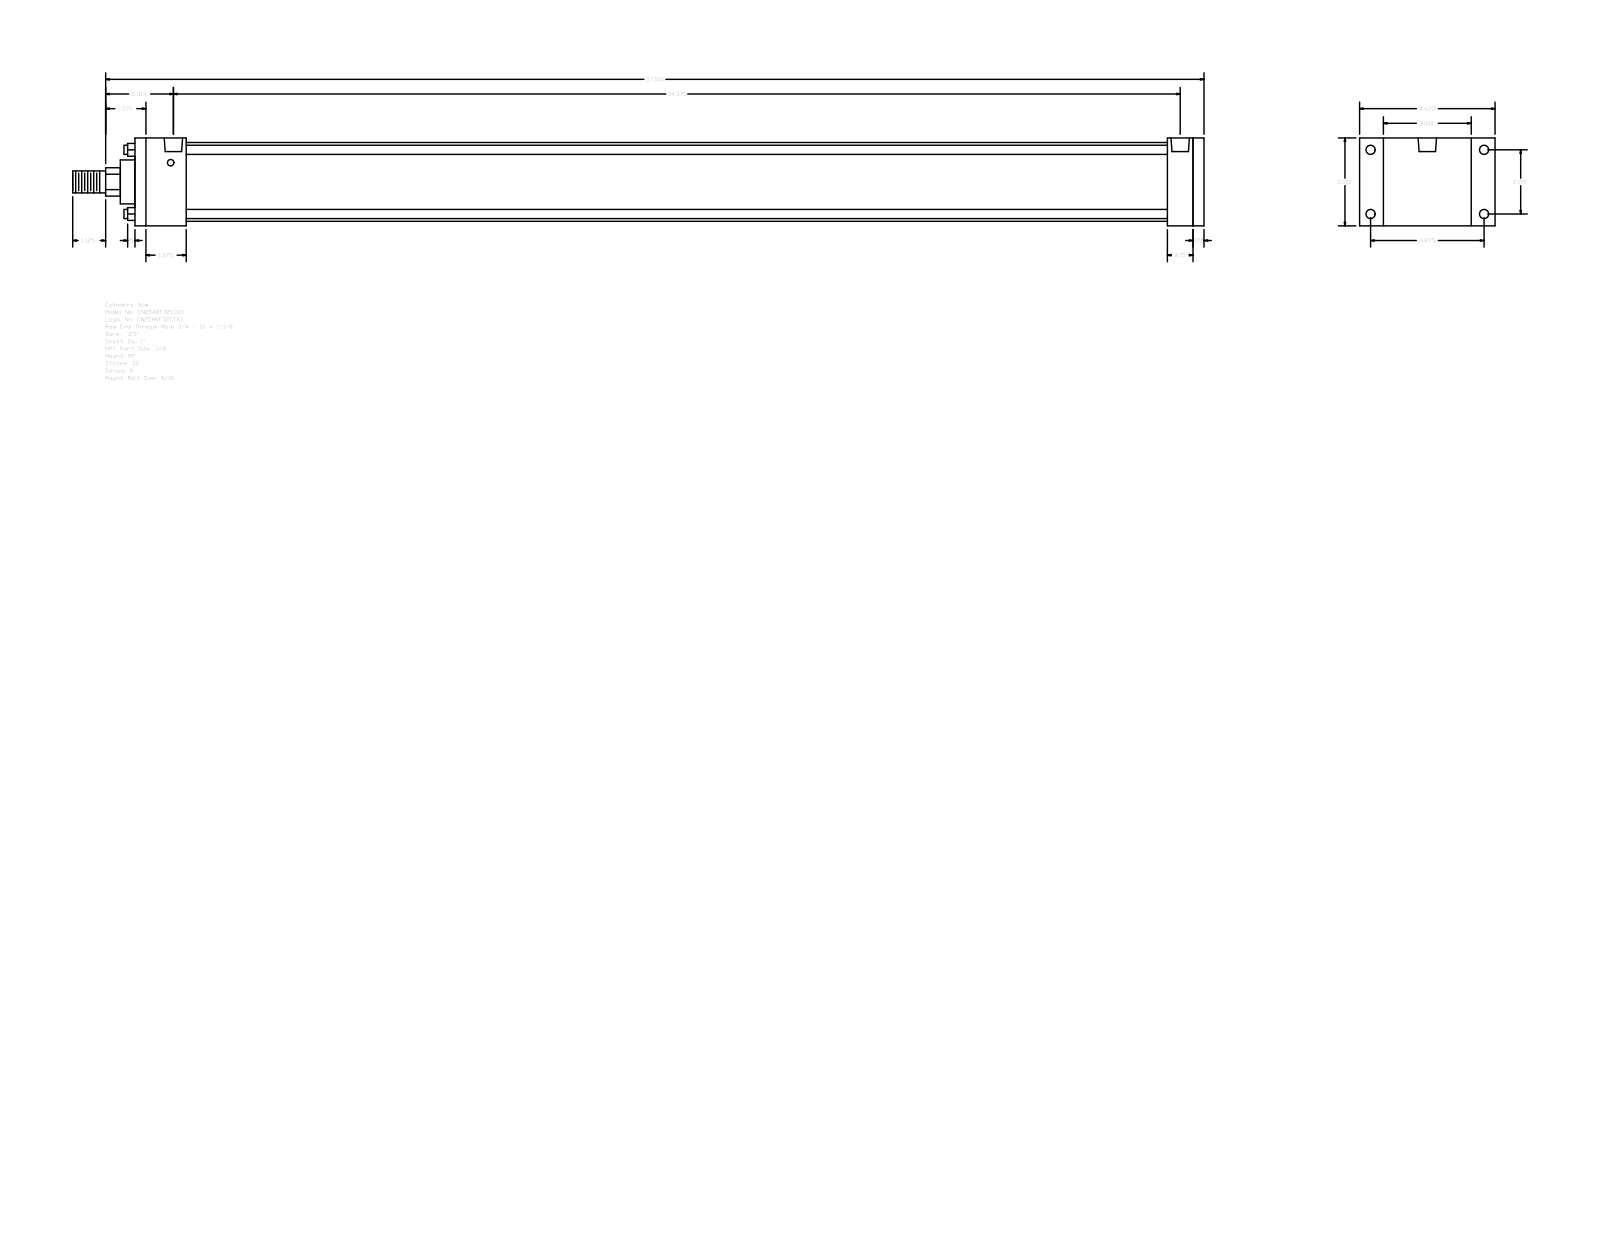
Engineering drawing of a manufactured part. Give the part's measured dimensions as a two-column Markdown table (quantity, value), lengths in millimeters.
| quantity | value |
| --- | --- |
| part name | A_RF__0250_1 |
| STEP written by | GSSL Pune (CONFIG_CONTROL_DESIGN) |
| units | millimeters |
| bodies | 0 solids, 92 faces (64 planar, 28 cylindrical, 0 other) |
| overall size | 981.08 × 117.47 × 76.2 |
| round holes (diameter × count) | 5.56 × 4, 7.94 × 4, 15.93 × 2 |
| round bosses / shafts (diameter × count) | 7.94 × 4, 68.33 × 1, 38.1 × 1, 25.4 × 1, 19.05 × 1 |
| partial cylindrical surfaces (radius × count) | 12.29 × 1 |
| main face-to-face distances | 76.2, 927.1, 9.52, 917.58, 44.45, 895.35, 850.9, 873.13, 882.65, 22.23 |
| hole center spacings | 2.38, 55.62, 98.42, 113.05, 875.5, 877.88, 873.12 |
